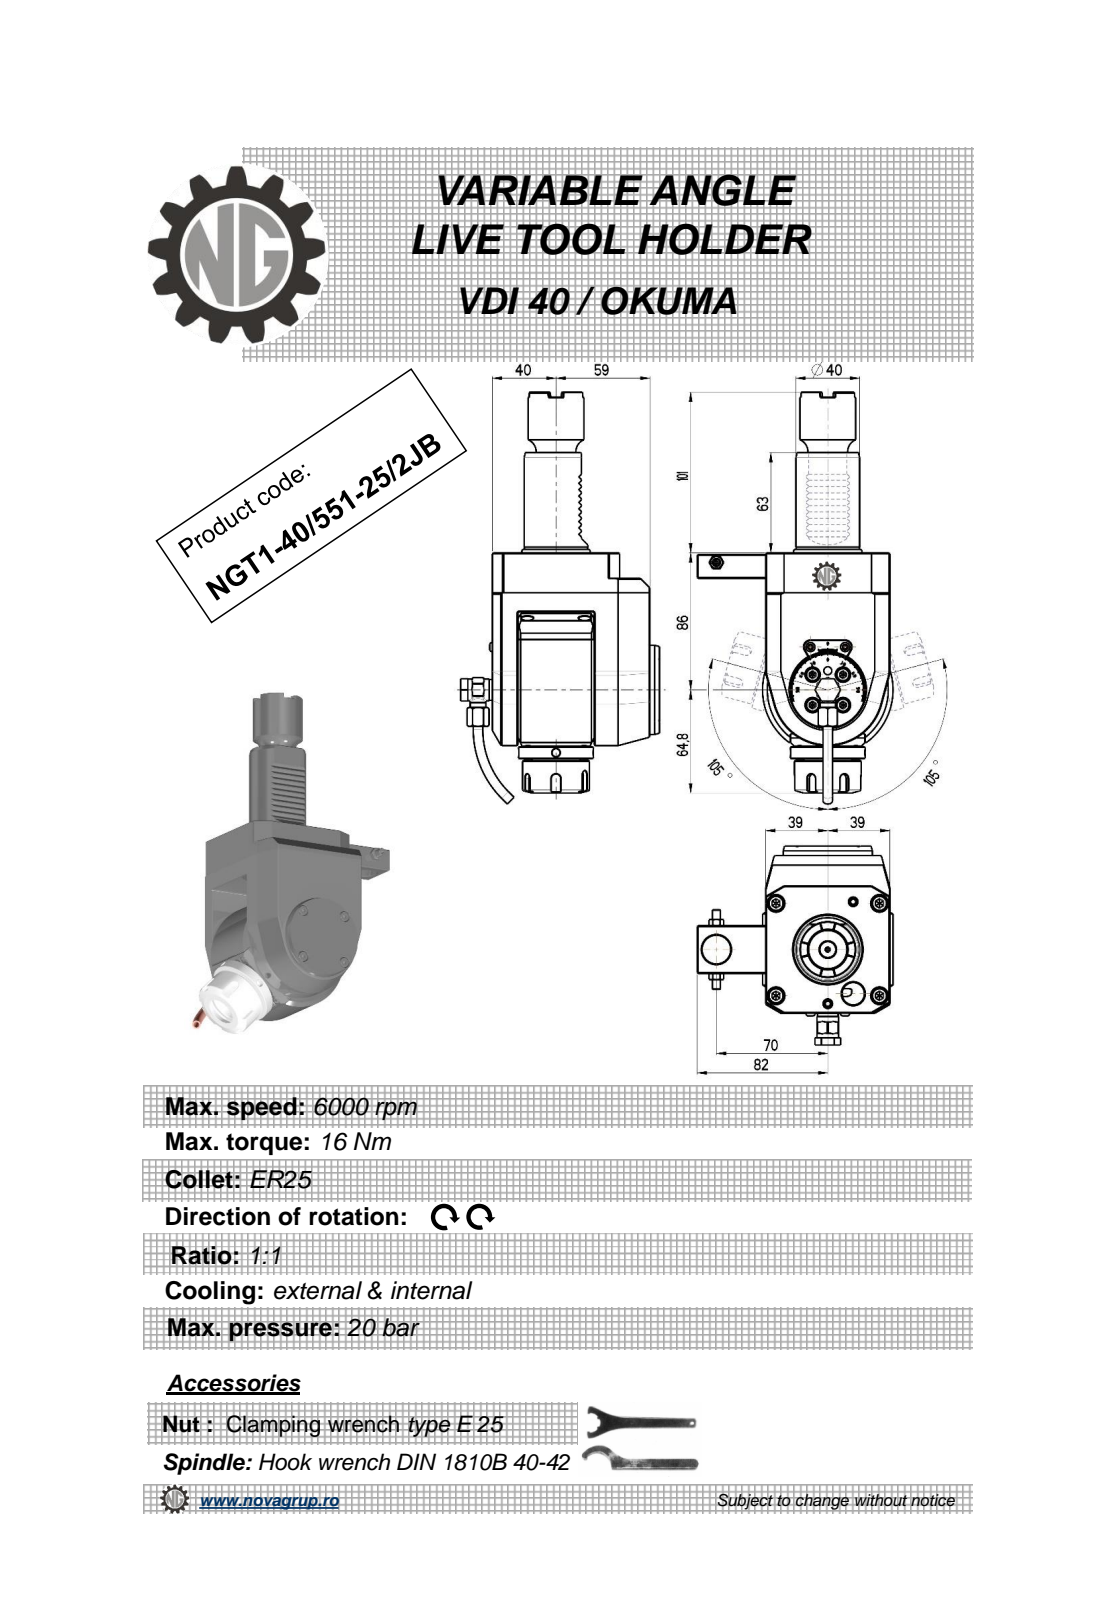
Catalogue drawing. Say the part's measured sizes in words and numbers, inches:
The part is named "NGT1_40_551_25_2JB". Its 3-D file was written by "PRO/ENGINEER BY PARAMETRIC TECHNOLOGY CORPORATION, 2010280 (CONFIG_CONTROL_DESIGN)". It is 1 solid with 617 faces: 258 planar, 138 cylindrical and 221 other. Overall it measures 10.184 by 4.917 by 4.843 inches. Its volume is 59.29 cubic inches and its surface area 139.1 square inches. Round holes: 3 of diameter 0.157, 2 of diameter 0.197, 1 of diameter 0.118, 1 of diameter 0.165, 1 of diameter 0.244, 1 of diameter 0.354, 1 of diameter 0.374, 1 of diameter 0.394, 1 of diameter 0.433, 1 of diameter 0.709, 1 of diameter 0.799, 1 of diameter 0.984. Round bosses or shafts: 2 of diameter 0.236, 2 of diameter 0.224, 1 of diameter 2.205, 1 of diameter 1.85, 1 of diameter 1.654, 1 of diameter 1.575, 1 of diameter 1.417, 1 of diameter 1.378. Partial cylindrical surfaces (rounded edges, fillets, slot ends): 12 of radius 0.01, 10 of radius 0.012, 5 of radius 0.118, 4 of radius 0.02, 2 of radius 0.039, 2 of radius 0.394, 1 of radius 0.303, 1 of radius 1.378. The main face-to-face distances are 0.63, 1.457, 3.898, 2.52, 3.071, 0.236, 4.134, 0.039, 0.827, 0.984. The hole center spacings are 0.016, 1.553, 1.929, 1.945, 2.756, 3.364, 3.373, 4.185.
